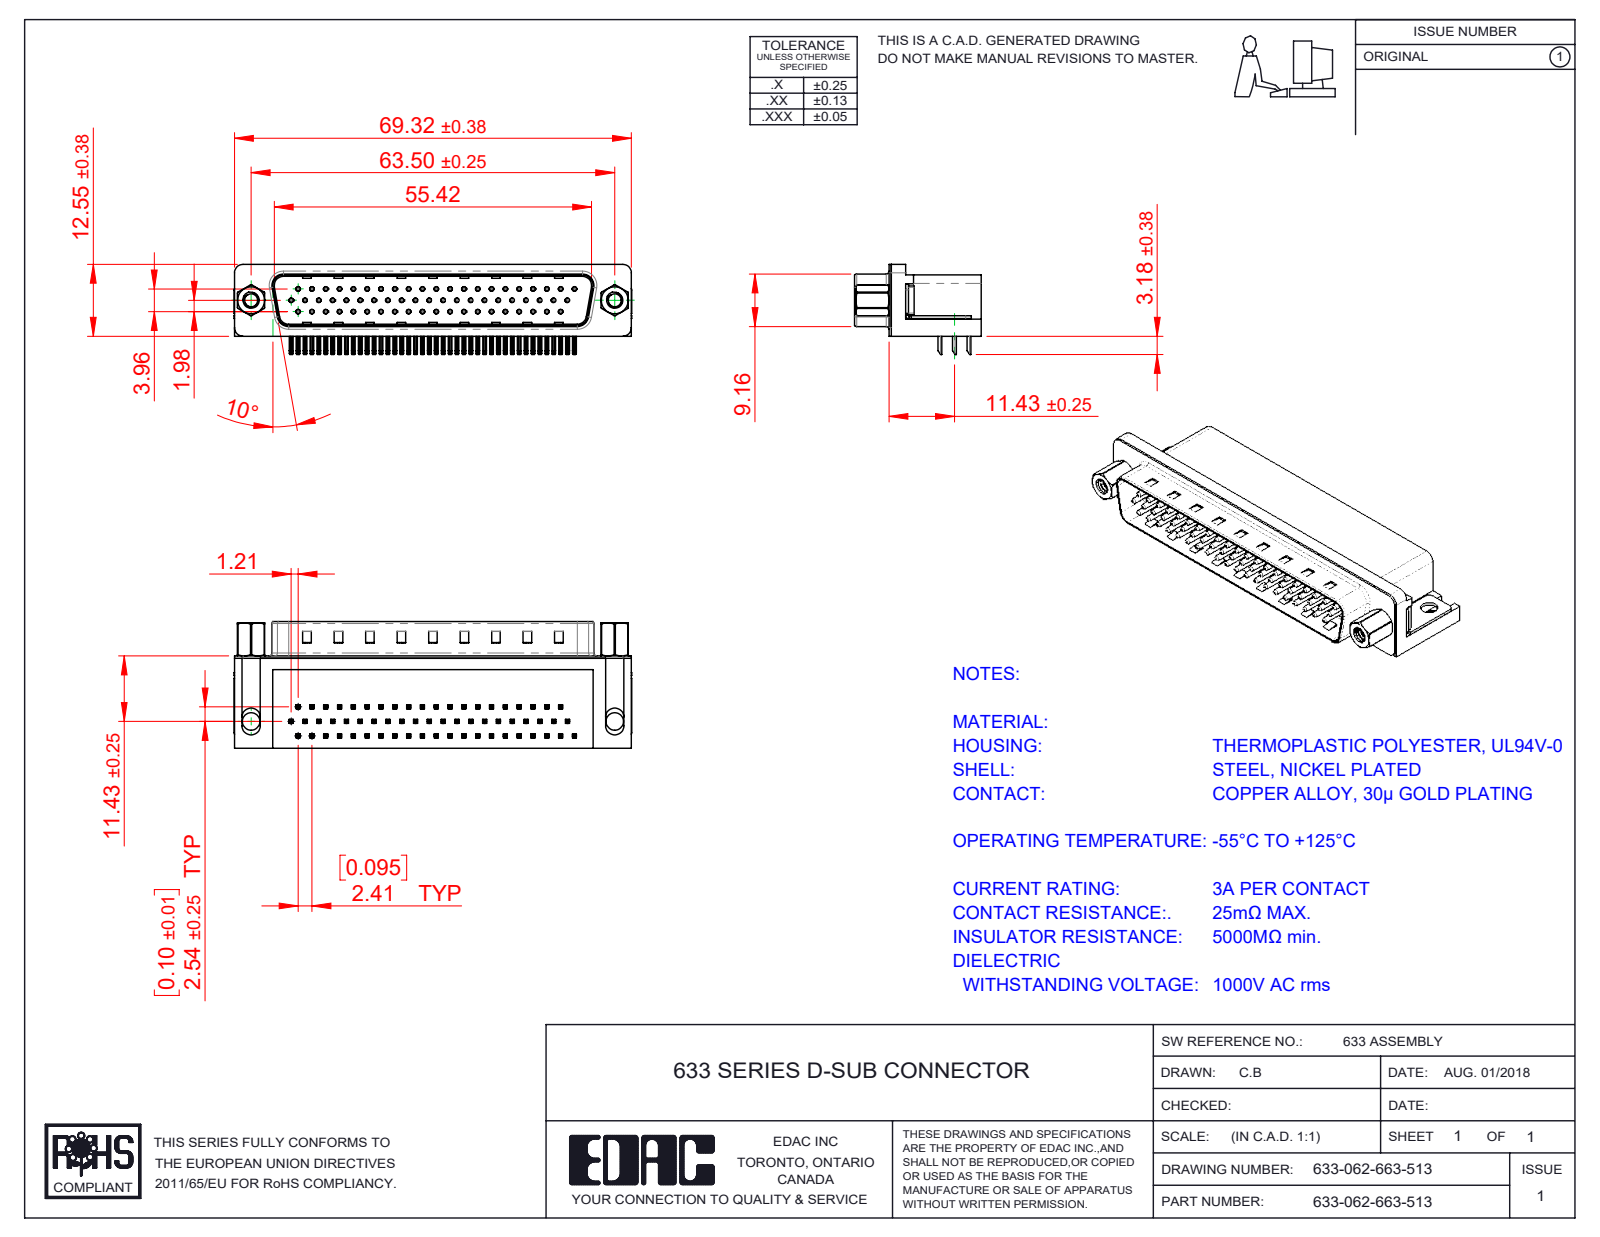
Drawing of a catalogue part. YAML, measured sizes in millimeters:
part_name: "633 Contact Top; 633 Thru Hole Board Mount; 633 Contact Middle; 633 Contact Bottom (+5 more)"
step_written_by: "SolidWorks 2016 (CONFIG_CONTROL_DESIGN)"
units: millimeters
bodies: {solids: 70, faces: 5194, planar: 3233, cylindrical: 1506, other: 455}
overall_size: [69.4, 22.1, 15.73]
volume: 11255
surface_area: 13846
round_holes:
  - {diameter: 0.35, count: 62}
  - {diameter: 0.8, count: 62}
  - {diameter: 2.26, count: 2}
  - {diameter: 2.29, count: 2}
  - {diameter: 3.05, count: 2}
  - {diameter: 4, count: 2}
  - {diameter: 4.8, count: 2}
  - {diameter: 5, count: 2}
round_bosses_or_shafts:
  - {diameter: 0.75, count: 62}
  - {diameter: 4.9, count: 2}
  - {diameter: 4.75, count: 2}
  - {diameter: 3.9, count: 2}
  - {diameter: 2.79, count: 2}
partial_cylinders:
  - {radius: 0.25, count: 256}
  - {radius: 0.12, count: 124}
  - {radius: 1, count: 16}
  - {radius: 0.5, count: 9}
  - {radius: 1.6, count: 8}
  - {radius: 1.5, count: 7}
  - {radius: 0.9, count: 4}
  - {radius: 2, count: 4}
face_to_face_distances: [0.4, 10.35, 15.7, 8.76, 2.9, 2.5, 2.54, 8.36, 16.1, 2.1]
hole_center_spacings: [2.41, 4.82, 7.24, 9.65, 14.48, 16.89, 4.83, 7.23]
